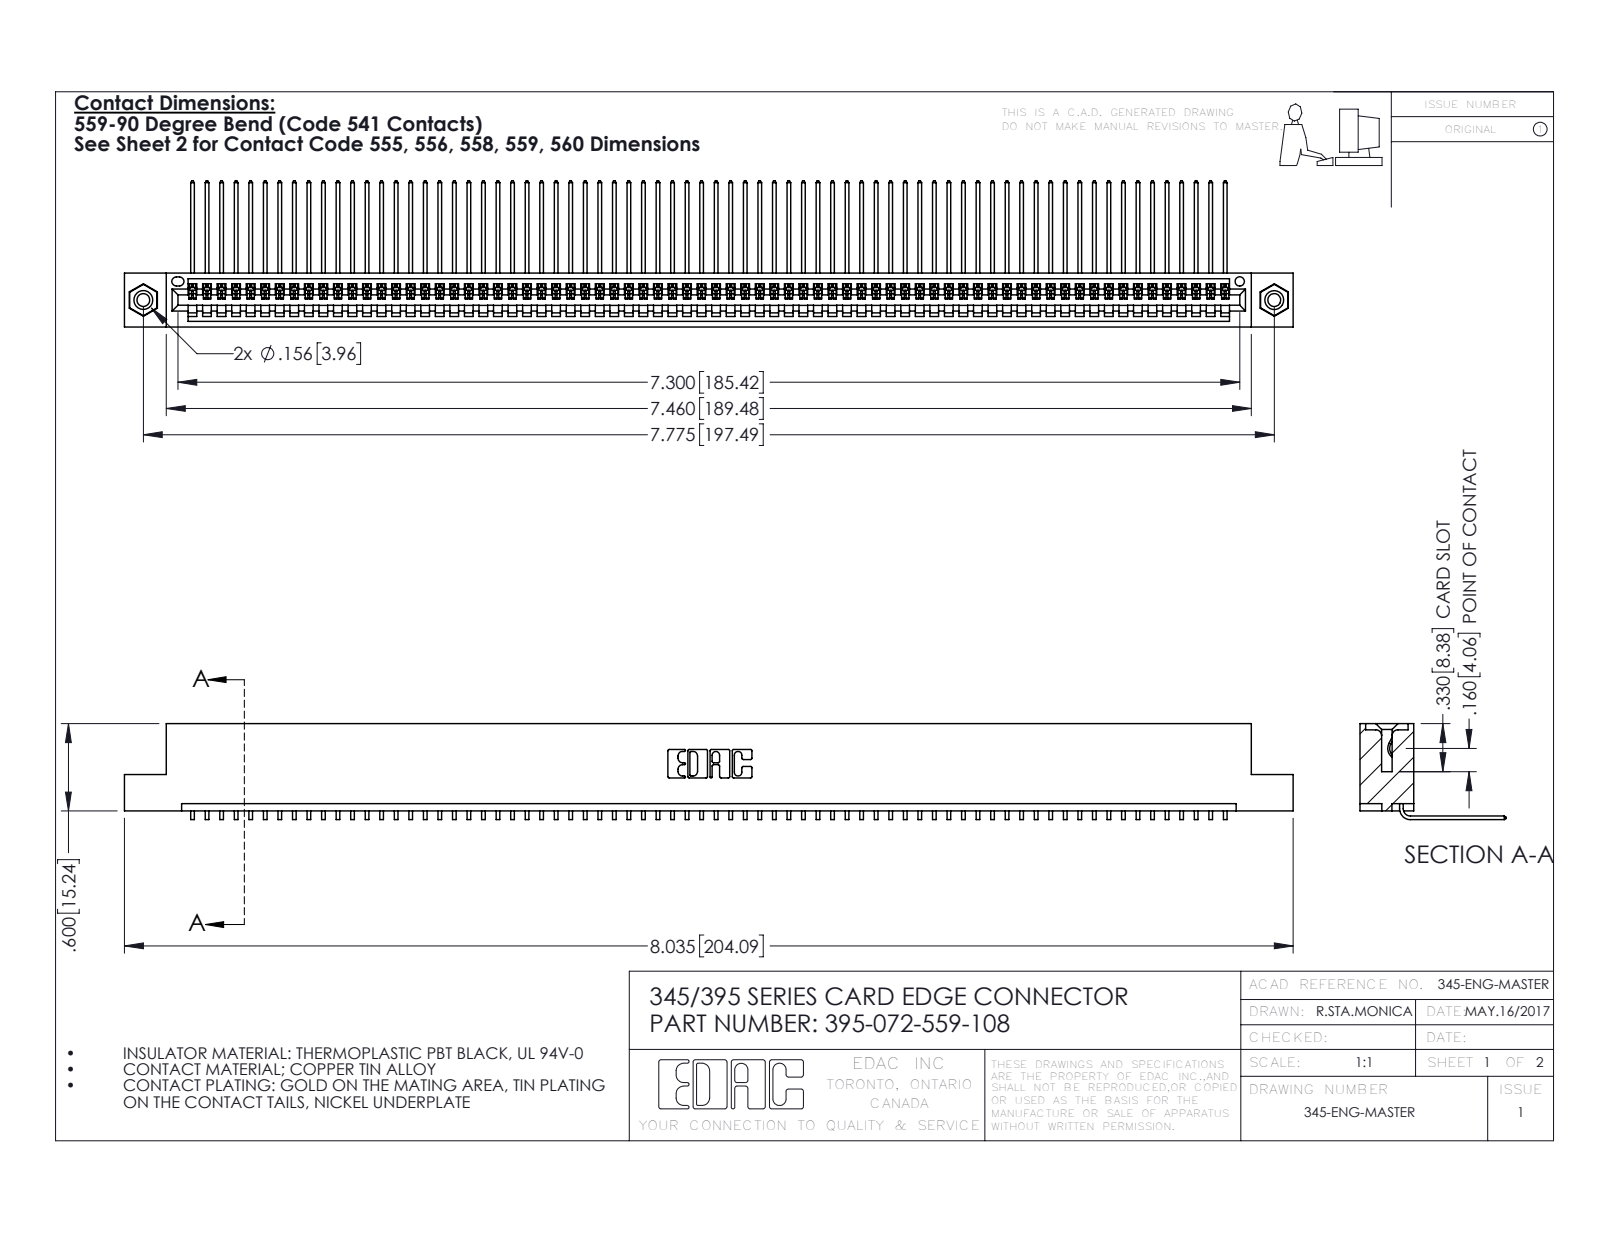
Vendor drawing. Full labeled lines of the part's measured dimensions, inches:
Part name (STEP PRODUCT): 345-250-001_345-250-003-102; 345 Part_Flush Mounting Lugs - 0.156 Dia-TI; 345-292-001_558 559 Tail - 1; 395-072-559-108
STEP written by: SolidWorks 2016 (CONFIG_CONTROL_DESIGN)
Units: inches
Bodies: 75 solids, 4506 faces (3136 planar, 1354 cylindrical, 16 other)
Overall size (bounding box): 8.035 × 1.005 × 0.659
Volume: 1.212 in³ · Surface area: 43.76 in²
Round holes (diameter × count): ⌀0.089 ×2, ⌀0.125 ×2, ⌀0.156 ×2, ⌀0.064 ×1
Round bosses / shafts (diameter × count): ⌀0.155 ×2
Partial cylindrical surfaces — rounded edges, fillets, slot ends (radius × count): R0.006 ×144, R0.01 ×22, R0.007 ×6, R0.031 ×6, R0.026 ×3, R0.031 ×2, R0.04 ×2, R0.014 ×1
Main face-to-face distances: 0.072, 0.298, 0.37, 0.2, 0.098, 0.272, 0.025, 0.225, 0.149, 0.072
Hole centre spacings: 0.27, 7.539, 7.775
